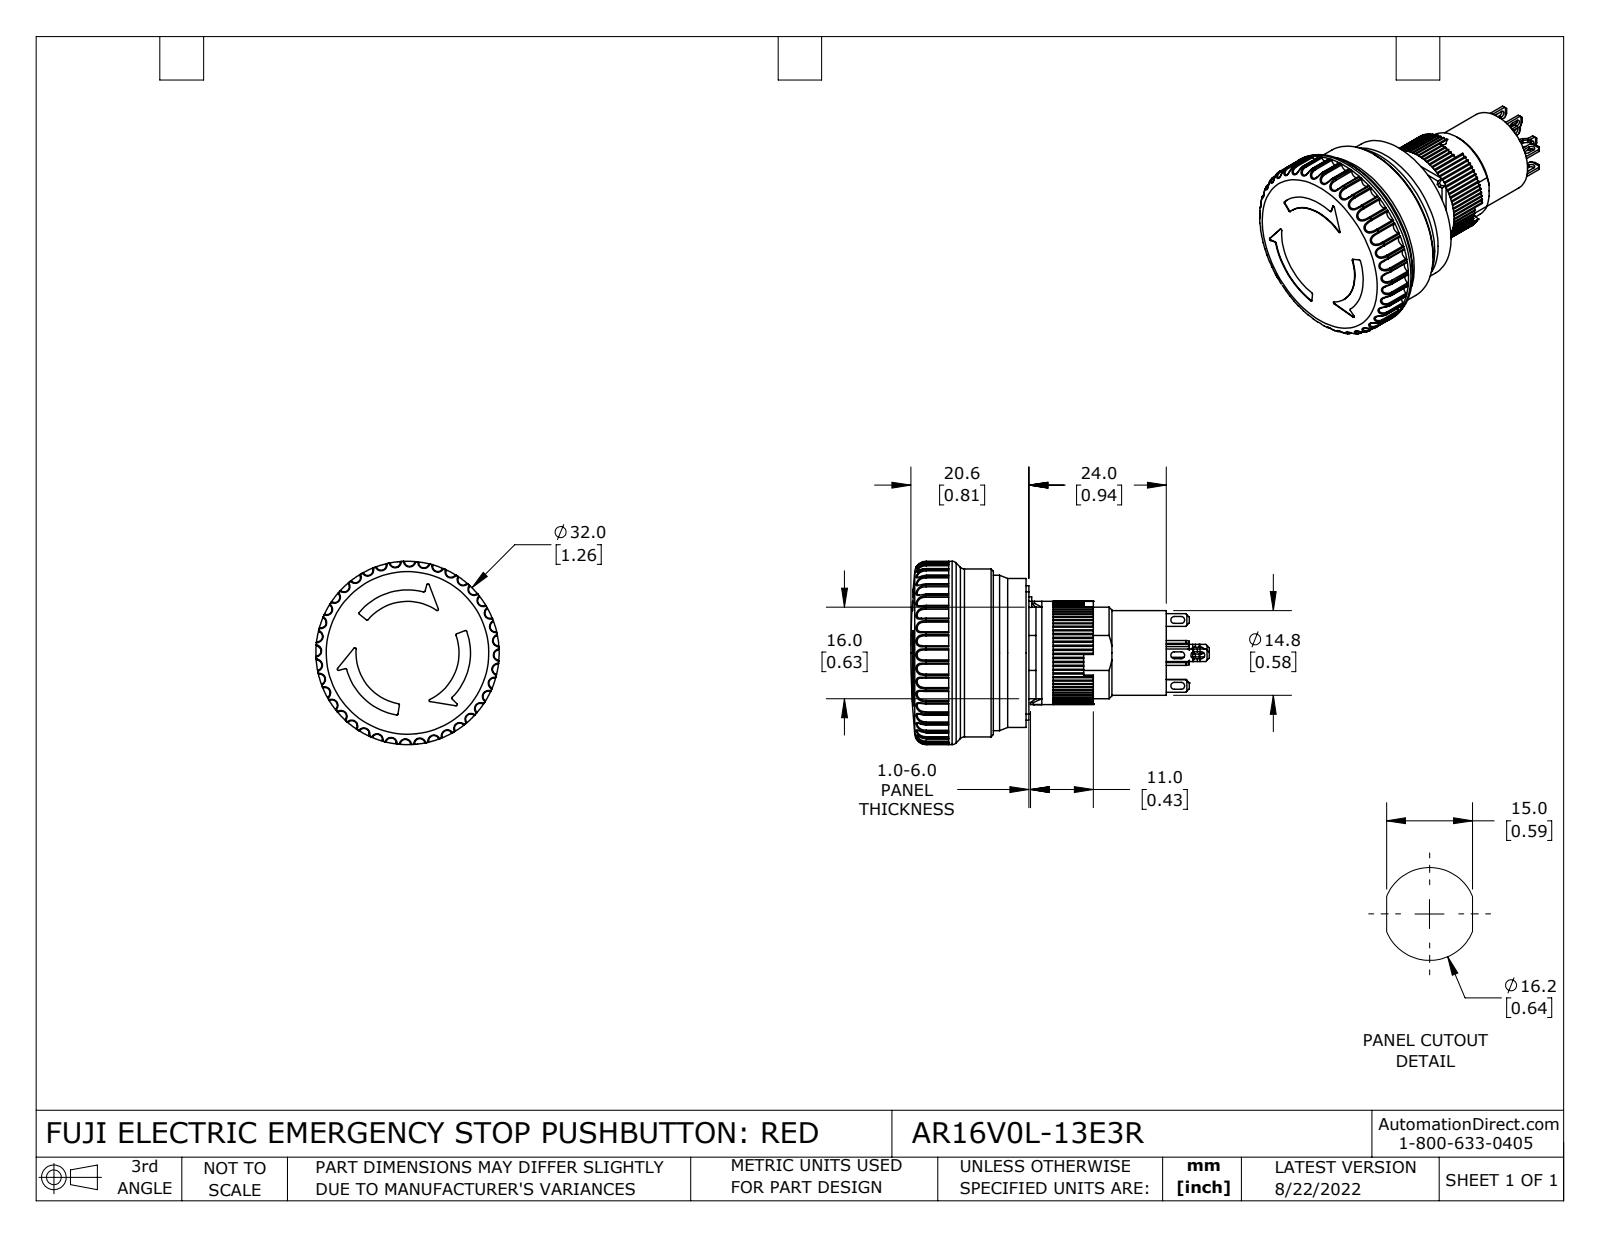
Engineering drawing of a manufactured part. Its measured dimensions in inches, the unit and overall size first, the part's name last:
Units: inches
Overall size (bounding box): 2.051 × 1.26 × 1.26
Round holes (diameter × count): ⌀0.583 ×1, ⌀0.63 ×1, ⌀1.069 ×1
Round bosses / shafts (diameter × count): ⌀1.26 ×1, ⌀1.154 ×1, ⌀1.024 ×1, ⌀0.858 ×1, ⌀0.709 ×1, ⌀0.236 ×1
Partial cylindrical surfaces — rounded edges, fillets, slot ends (radius × count): R0.008 ×80, R0.01 ×80, R0.035 ×40, R0.024 ×16, R0.02 ×8, R0.01 ×4, R0.029 ×4, R0.039 ×2
Main face-to-face distances: 0.421, 0.53, 0.108, 0.039, 0.02, 0.069, 0.856, 0.49, 0.089, 0.049
Volume: 1.124 in³ · Surface area: 13.68 in²
Bodies: 7 solids, 1001 faces (540 planar, 387 cylindrical, 74 other)
Part name (STEP PRODUCT): AR16V0L-13E3R
STEP written by: SolidWorks 2021 (CONFIG_CONTROL_DESIGN)
